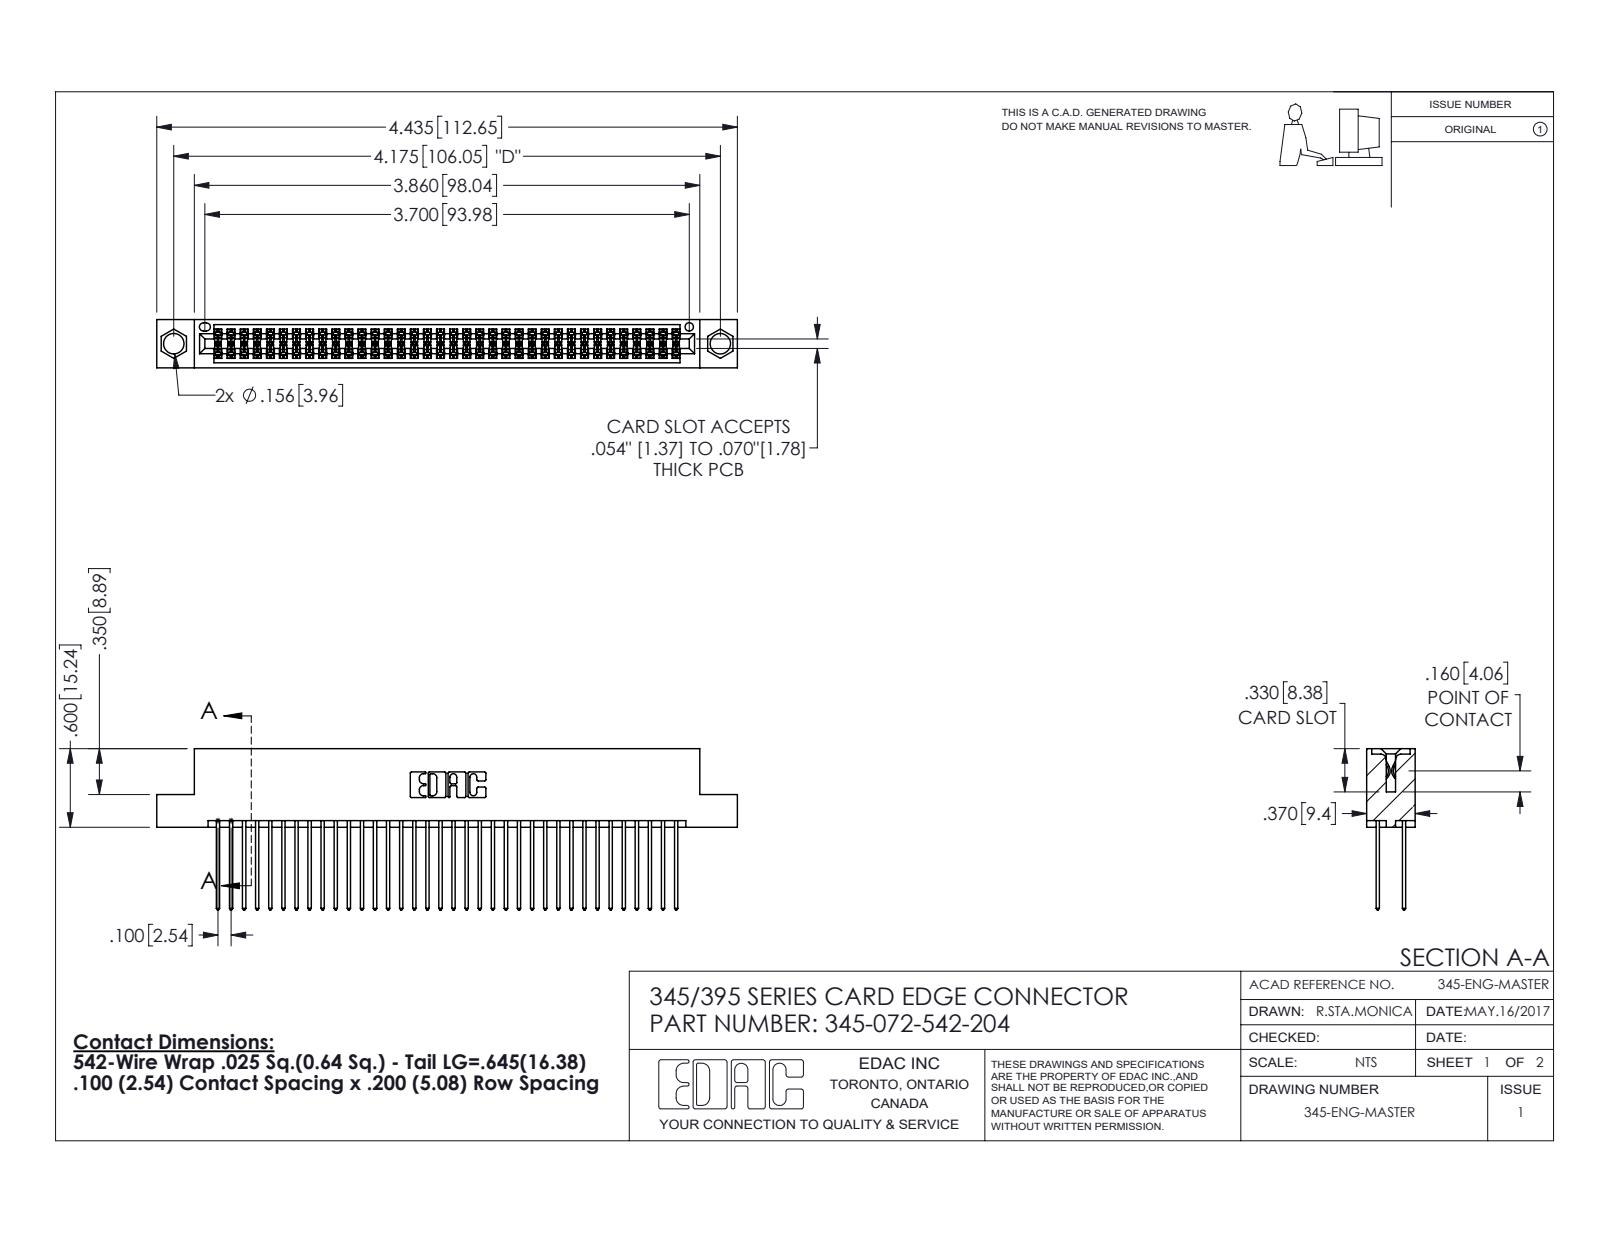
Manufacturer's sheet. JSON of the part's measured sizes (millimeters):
{"part_name": "345-072-542-204; 345 Part_Flush Mounting Lugs - 0.156 Dia-TI; 345-292-001_345-293-142", "step_written_by": "SolidWorks 2020 (CONFIG_CONTROL_DESIGN)", "units": "millimeters", "bodies": {"solids": 73, "faces": 3740, "planar": 2470, "cylindrical": 1270, "other": 0}, "overall_size": [112.6, 31.3, 9.4], "volume_mm3": 11100, "surface_area_mm2": 17740, "round_holes": [[4, 2], [1.6, 1]], "partial_cylinders_radius": [[0.2, 108], [0.3, 72], [0.3, 22], [0.2, 6], [0.8, 6], [0.7, 3], [0.4, 2], [0.5, 2]], "face_to_face_distances": [7.6, 1.8, 5.1, 2.5, 6.9, 0.6, 9.4, 5.7, 4.4, 3.8], "hole_center_spacings": [6.9, 100.1, 106]}
